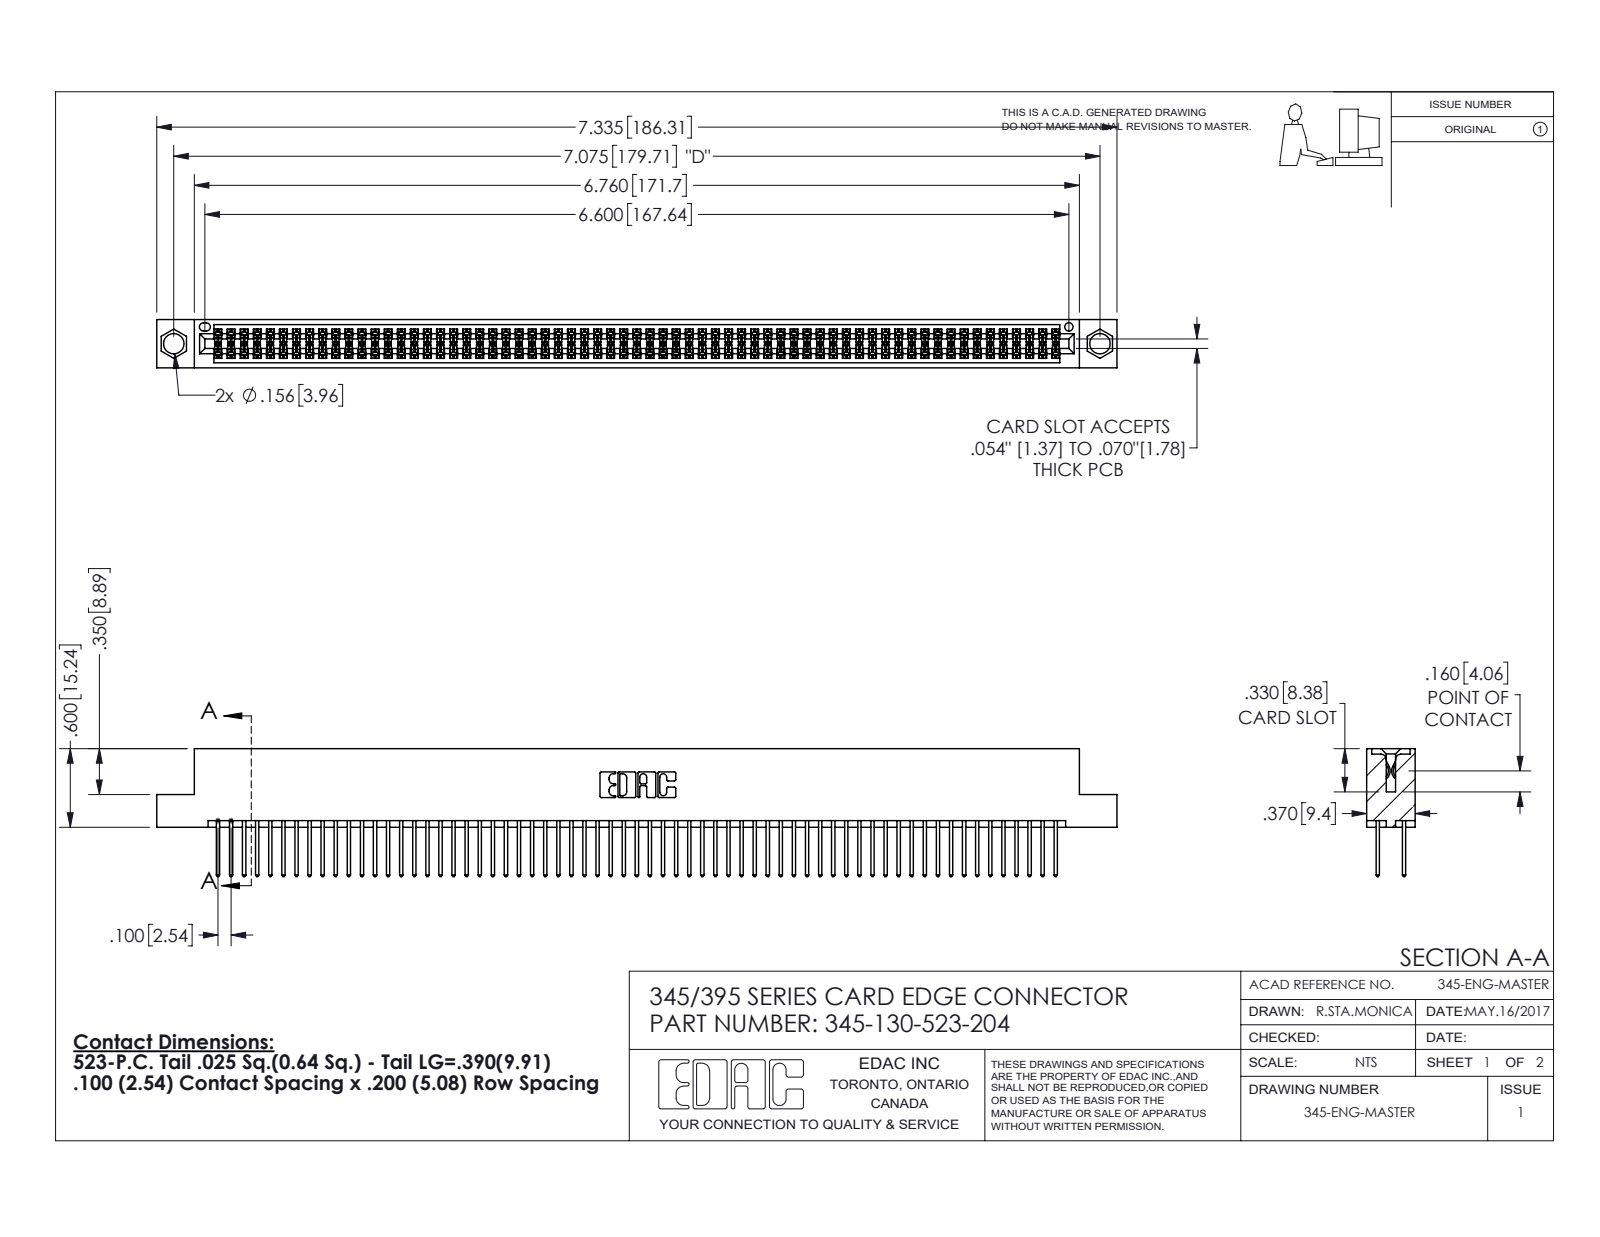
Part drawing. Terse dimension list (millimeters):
name: 345-130-523-204; 345 Part_Flush Mounting Lugs - 0.156 Dia-TI; 345-292-001_345-293-123
written by: SolidWorks 2020 (CONFIG_CONTROL_DESIGN)
unit: mm
bodies: 131 solids, 6640 faces (4384 planar, 2256 cylindrical, 0 other)
size: 186.3 × 24.8 × 9.4
volume: 18 470 mm³; area: 28 800 mm²
holes: 2× ⌀4, 1× ⌀1.6
rounds: 195× R0.2, 130× R0.3, 22× R0.3, 6× R0.2, 6× R0.8, 3× R0.7, 2× R0.4, 2× R0.5
face distances: 7.6, 1.8, 5.1, 2.5, 6.9, 0.6, 9.4, 5.7, 4.4, 3.8
hole spacings: 6.9, 173.7, 179.7
